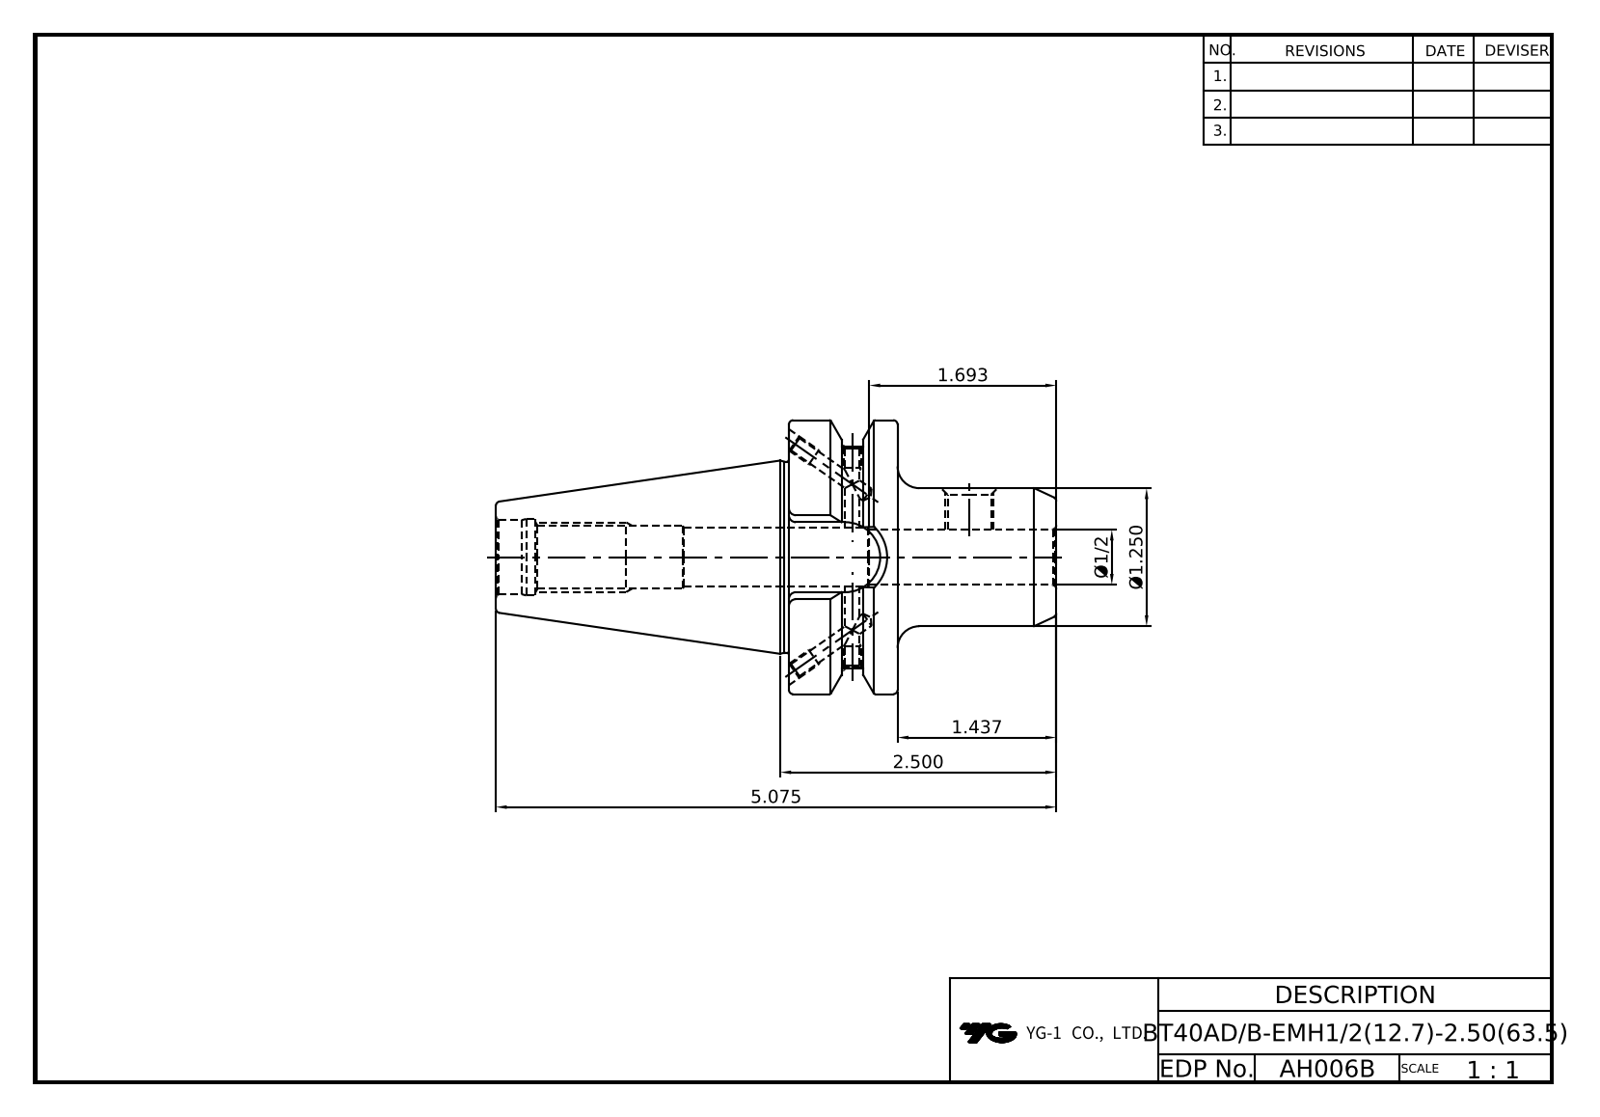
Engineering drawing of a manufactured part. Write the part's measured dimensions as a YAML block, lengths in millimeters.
part_name: "LO-BT40ADB-EMH12.7-63.5"
step_written_by: "Autodesk Inventor 2022 (AUTOMOTIVE_DESIGN)"
units: millimeters
bodies: {solids: 1, faces: 66, planar: 19, cylindrical: 27, other: 20}
overall_size: [128.9, 63, 63]
volume: 142770
surface_area: 27966
round_holes:
  - {diameter: 3.24, count: 4}
  - {diameter: 4, count: 4}
  - {diameter: 9.73, count: 1}
  - {diameter: 12.7, count: 1}
  - {diameter: 13.5, count: 1}
  - {diameter: 13.84, count: 1}
  - {diameter: 17, count: 1}
  - {diameter: 17.6, count: 1}
round_bosses_or_shafts:
  - {diameter: 63, count: 1}
  - {diameter: 52.6, count: 1}
  - {diameter: 44, count: 1}
  - {diameter: 31.75, count: 1}
partial_cylinders:
  - {radius: 8.05, count: 1}
face_to_face_distances: [25, 61.5, 36.5, 45.2, 16.1, 67.4, 92.4, 128.9, 84.5, 17.1]
